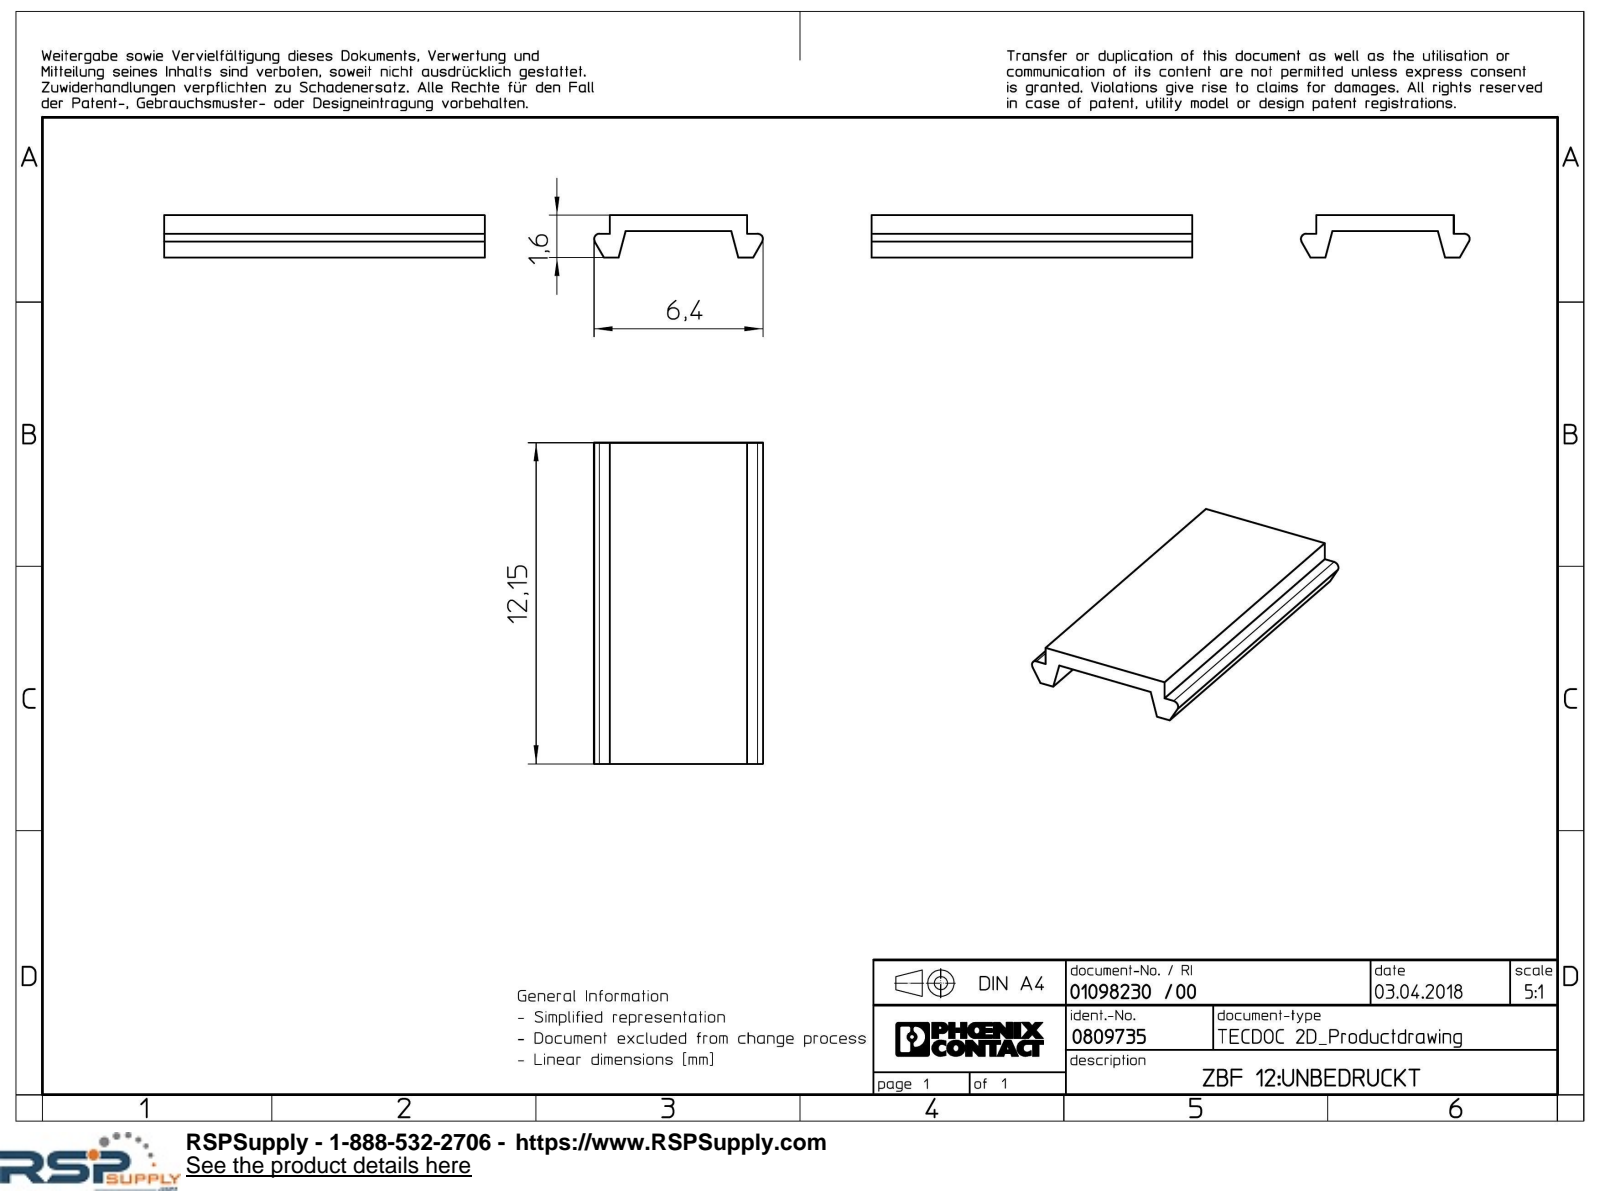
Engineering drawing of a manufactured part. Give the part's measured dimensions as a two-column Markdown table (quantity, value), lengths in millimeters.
| quantity | value |
| --- | --- |
| part name | ZBF_12_UNBEDRUCKT-select |
| STEP written by | Creo Elements/Direct Modeling 18.1I 14-Aug-2016 (C) Parametric Technology GmbH (AUTOMOTIVE_DESIGN) |
| units | millimeters |
| bodies | 1 solid, 16 faces (14 planar, 2 cylindrical, 0 other) |
| overall size | 12.15 × 6.4 × 1.6 |
| volume | 59 mm³ |
| surface area | 214 mm² |
| partial cylindrical surfaces (radius × count) | 0.2 × 2 |
| main face-to-face distances | 0.6, 1, 1.6, 0.9, 0.7, 5.2, 12.15 |
